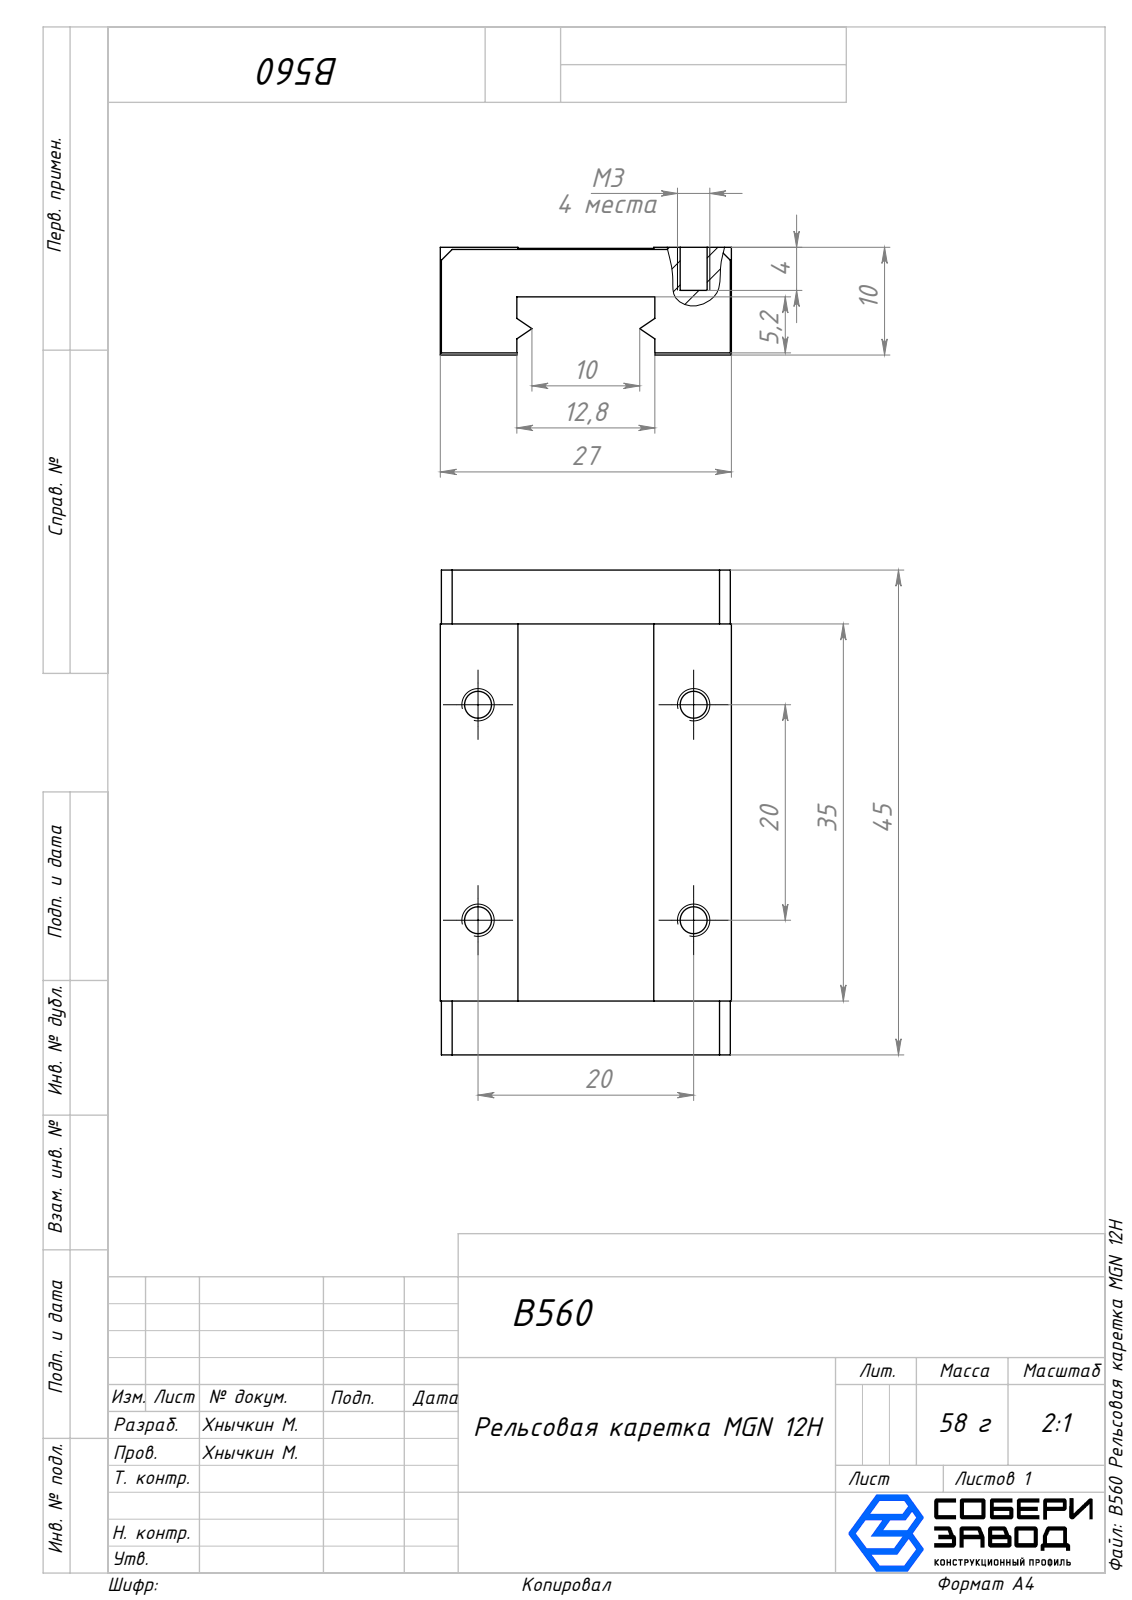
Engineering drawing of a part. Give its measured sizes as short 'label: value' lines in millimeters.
name: B560 Рельсовая каретка MGN 12H.SLDPRT
written by: SolidWorks 2025 (AUTOMOTIVE_DESIGN)
unit: mm
bodies: 1 solid, 48 faces (40 planar, 8 cylindrical, 0 other)
size: 45 × 27 × 10
volume: 8 925 mm³; area: 4 459 mm²
holes: 4× ⌀2.5
face distances: 5.4, 4.6, 10, 4.5, 9.9, 9.8, 27, 7.1, 19.9, 4.4
hole spacings: 20, 28.28
